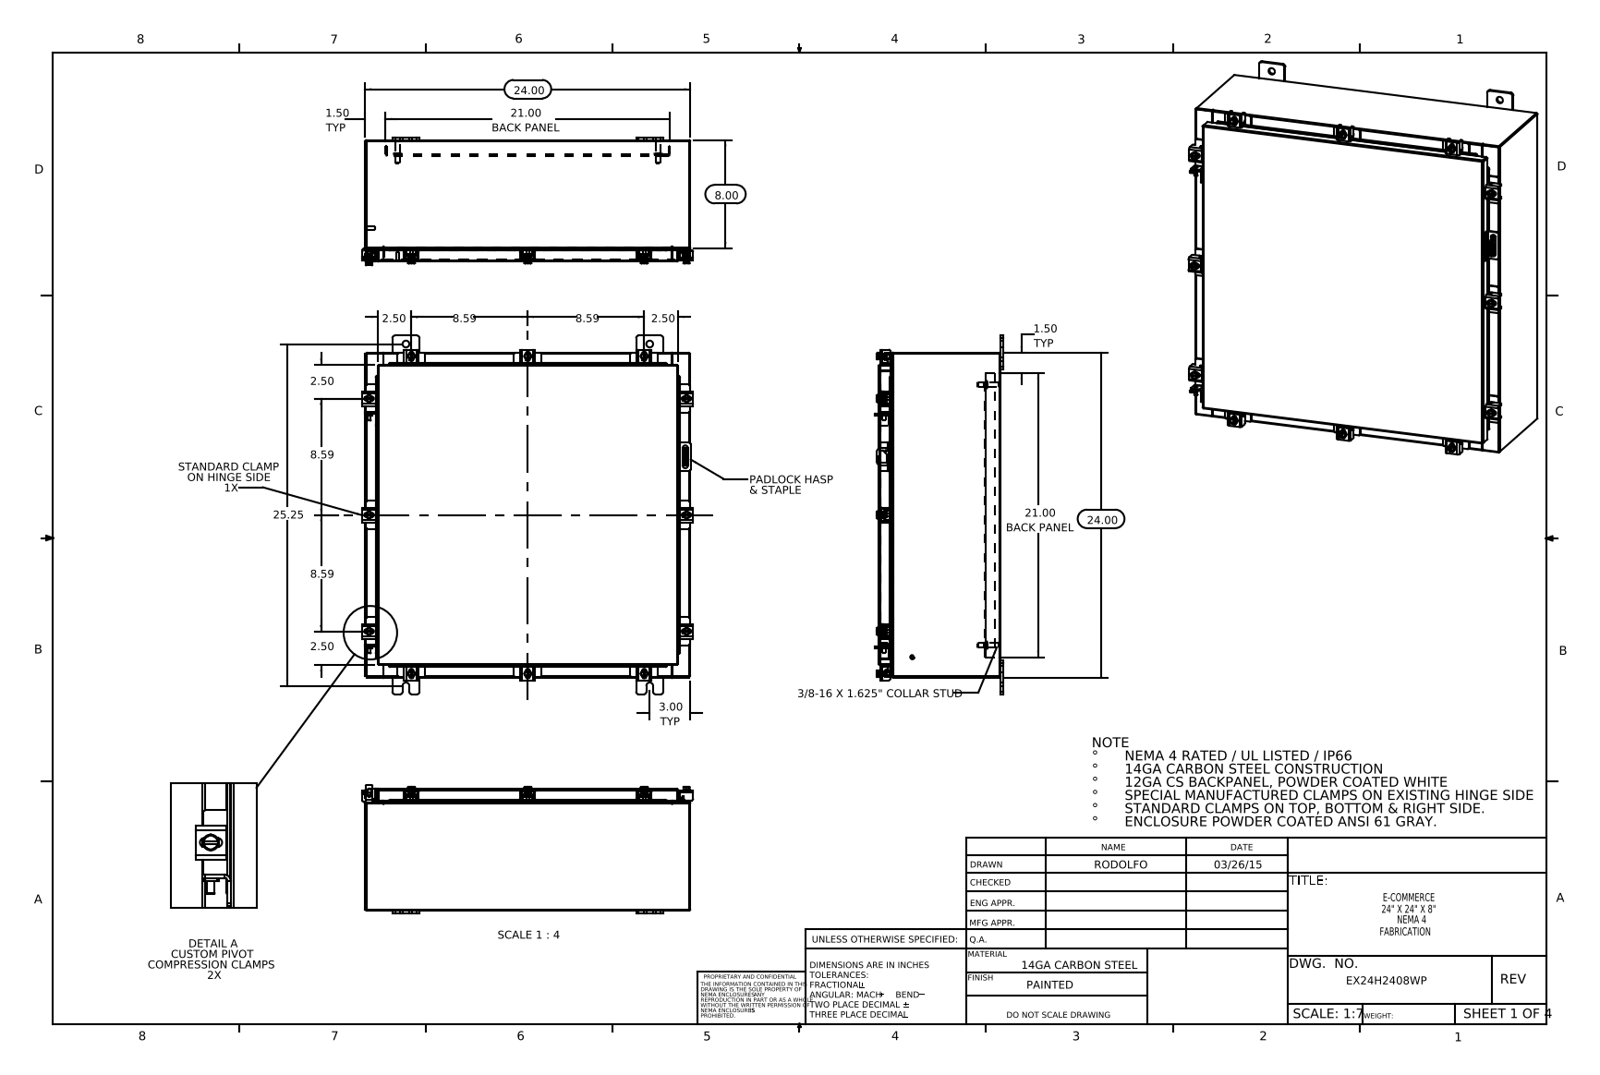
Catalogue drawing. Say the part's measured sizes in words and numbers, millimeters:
The part is named "EX24H2408WP Clamp Assembly; EX24H2408WP Backpanel; 22101002_RTP29; HW-CLN-NH-20330 (+8 more)". Its 3-D file was written by "SolidWorks 2014 (CONFIG_CONTROL_DESIGN)". It is 81 solids with 2018 faces: 1075 planar, 783 cylindrical and 160 other. Overall it measures 673.1 by 620.3 by 240.1 millimeters. Its volume is 3 548 000 cubic millimeters and its surface area 3 488 000 square millimeters. Round holes: 12 of diameter 5.4, 12 of diameter 6.6, 8 of diameter 12.7, 1 of diameter 3.2, 1 of diameter 6.4. Round bosses or shafts: 12 of diameter 12.7, 12 of diameter 6.4, 10 of diameter 10.1, 4 of diameter 15.9, 4 of diameter 9.5, 4 of diameter 8.4, 2 of diameter 8, 2 of diameter 6. Partial cylindrical surfaces (rounded edges, fillets, slot ends): 54 of radius 1.5, 24 of radius 0.3, 24 of radius 3.6, 24 of radius 4.8, 22 of radius 2.2, 22 of radius 3, 18 of radius 2.3, 17 of radius 1.3. The main face-to-face distances are 1.9, 226.1, 607.7, 228, 224.2, 2.6, 25.4, 27.3, 198.8, 200.7. The hole center spacings are 522.2, 59.4, 465.8, 543, 595.7, 112.5, 218.3, 218.3.
